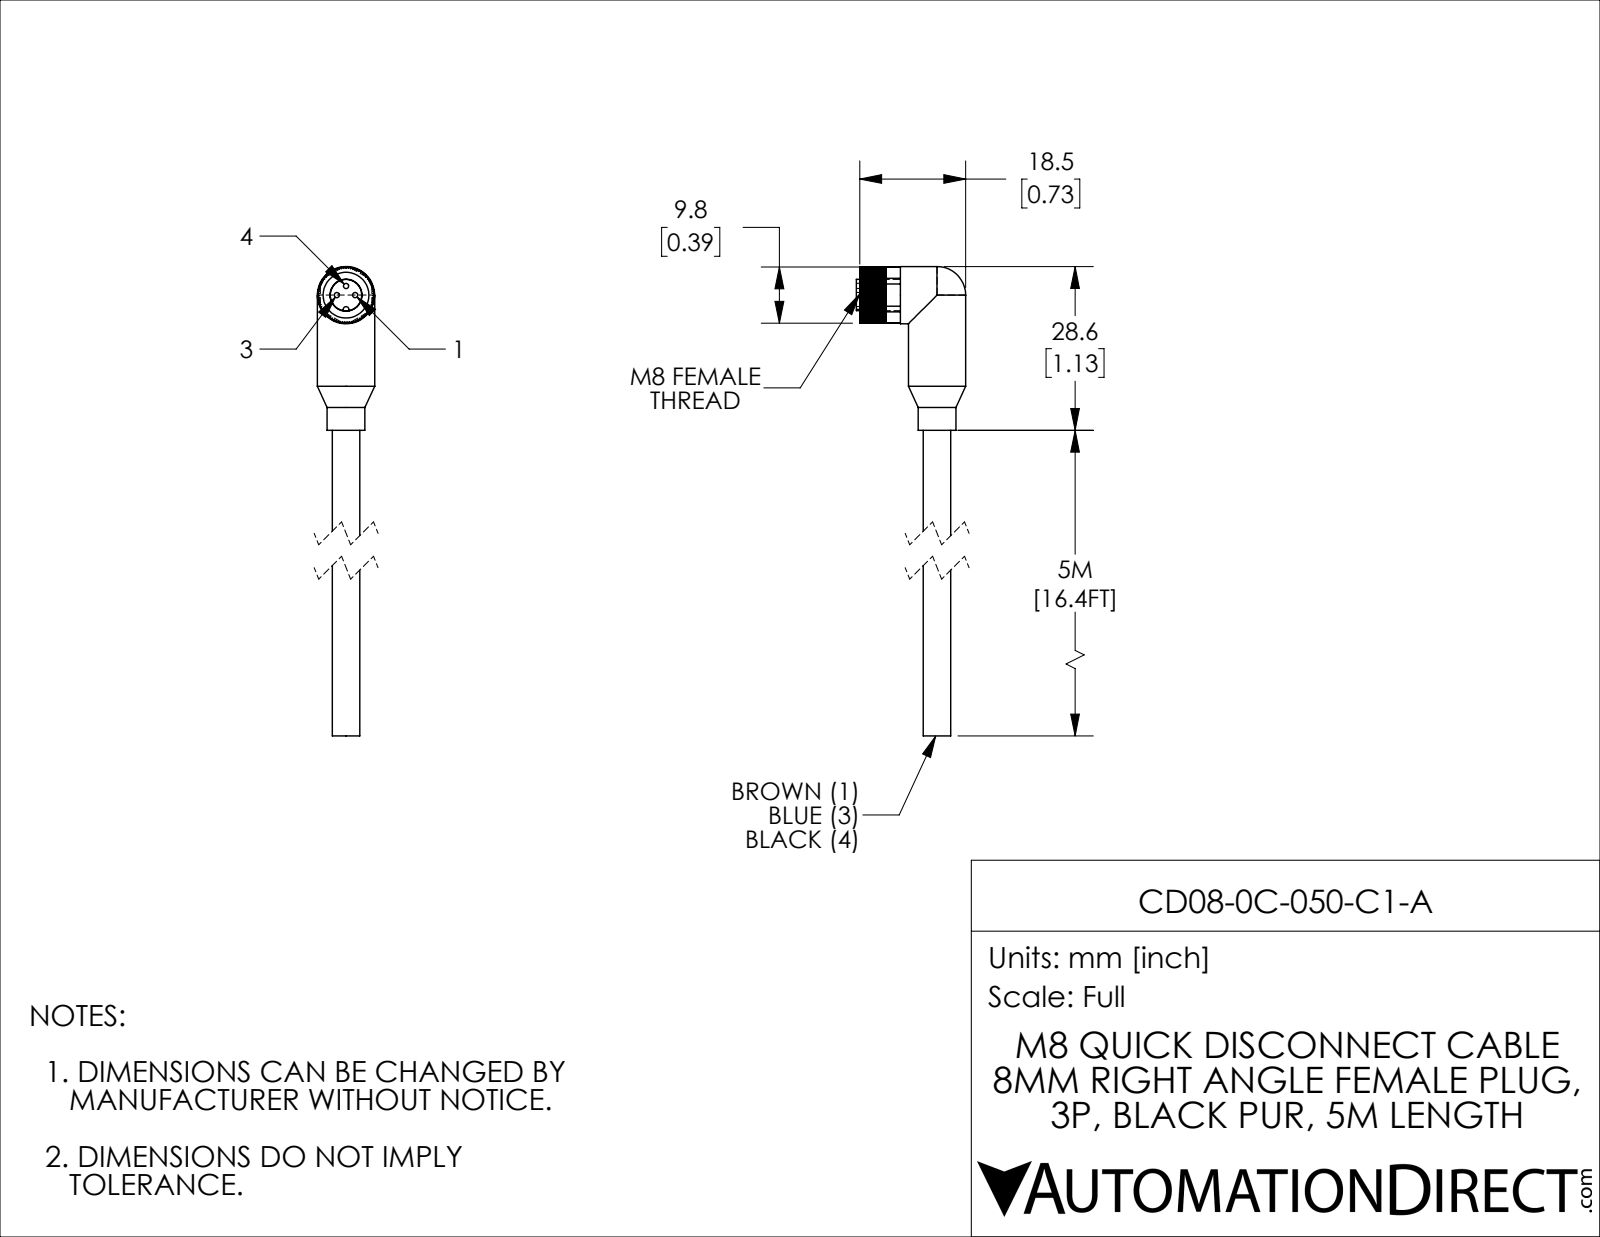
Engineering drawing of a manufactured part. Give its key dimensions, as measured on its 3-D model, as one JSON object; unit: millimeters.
{"part_name": "CD08-0C-050-C1-A", "step_written_by": "SolidWorks 2021 (CONFIG_CONTROL_DESIGN)", "units": "millimeters", "bodies": {"solids": 4, "faces": 307, "planar": 222, "cylindrical": 82, "other": 3}, "overall_size": [128.6, 19.1, 10], "volume_mm3": 4280, "surface_area_mm2": 3298, "round_holes": [[0.9, 3], [5.6, 1], [8, 1]], "round_bosses_or_shafts": [[10, 2], [6.6, 1], [5.5, 1], [4.8, 1]], "partial_cylinders_radius": [[0.5, 1], [4.9, 1]], "face_to_face_distances": [9, 0.6, 4.6, 3.1, 4, 7.1, 7.7, 100, 2.5, 5.2], "hole_center_spacings": [1.6, 2.3, 3.2]}
